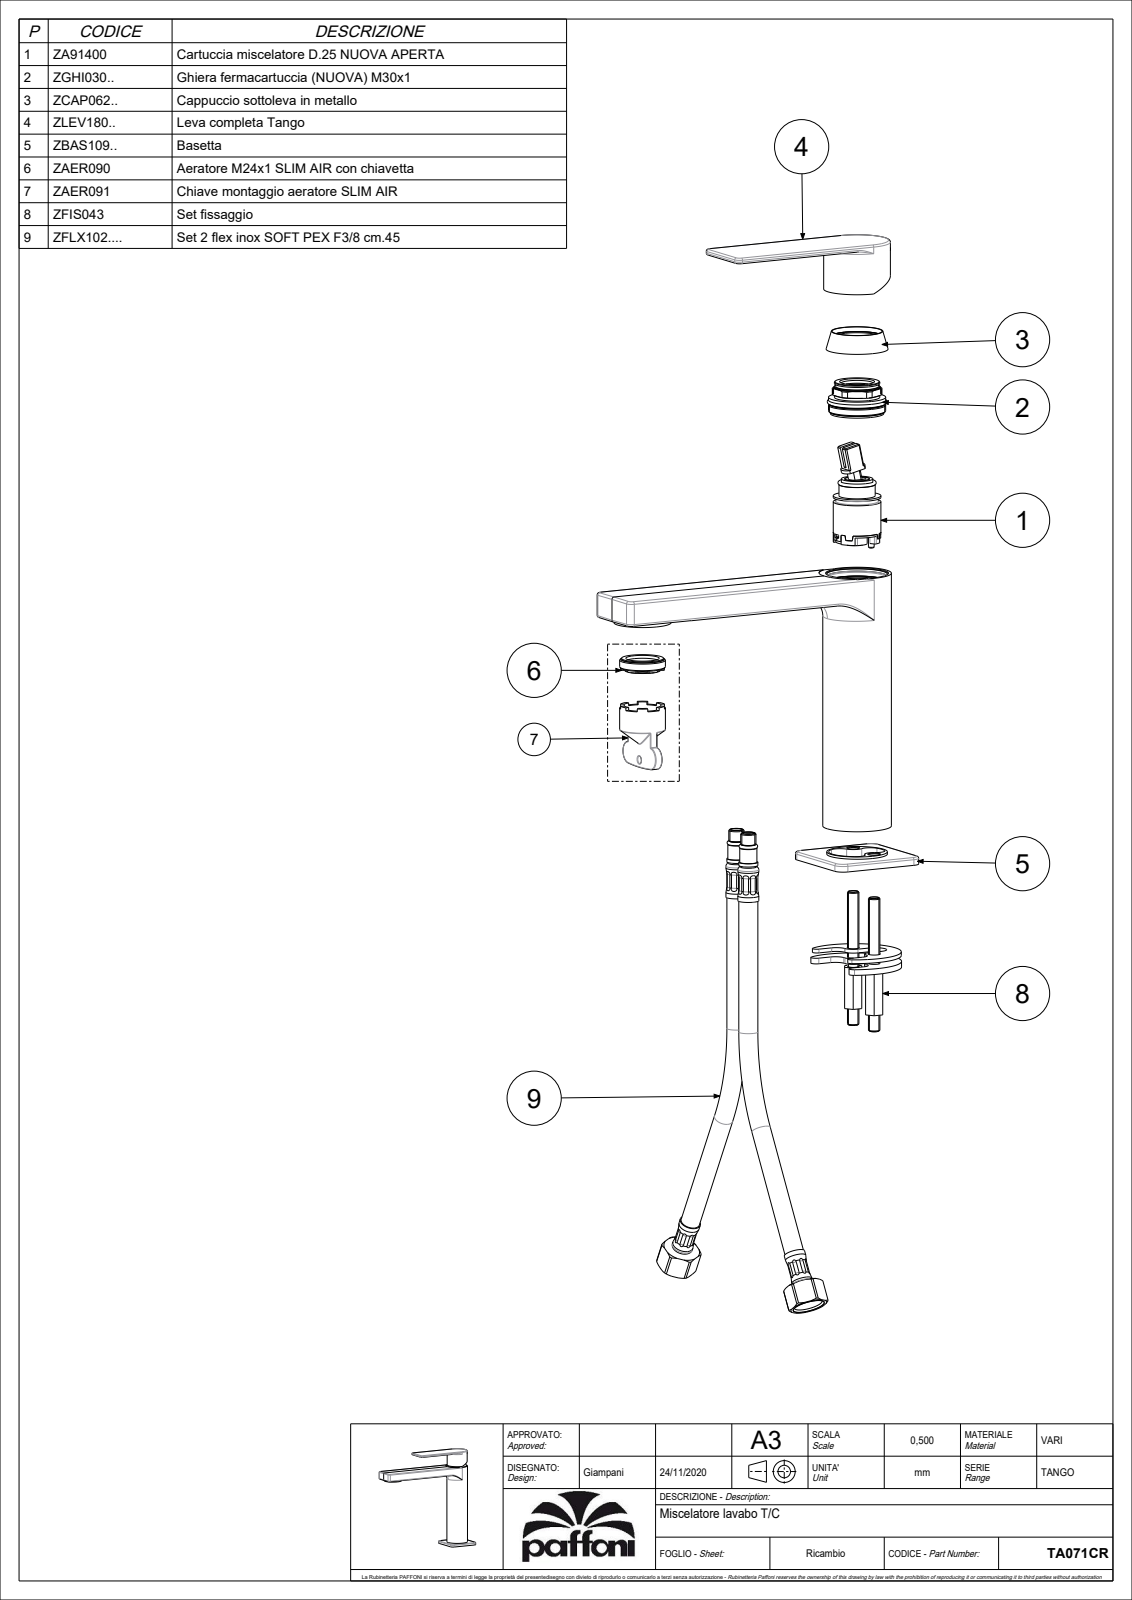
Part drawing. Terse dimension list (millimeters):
name: TA071CR
written by: CREO PARAMETRIC BY PTC INC, 2020044 (CONFIG_CONTROL_DESIGN)
unit: mm
bodies: 2 solids, 477 faces (132 planar, 162 cylindrical, 183 other)
size: 173.5 × 166.2 × 50
volume: 116 220 mm³; area: 72 907 mm²
holes: 2× ⌀4.2, 2× ⌀5, 2× ⌀6.2, 1× ⌀3, 1× ⌀17.5, 1× ⌀24.8, 1× ⌀26.2, 1× ⌀28, 1× ⌀29, 1× ⌀29.29, 1× ⌀30.6, 1× ⌀31.7
bosses: 1× ⌀41.8, 1× ⌀36, 1× ⌀35, 1× ⌀31.8, 1× ⌀30, 1× ⌀25, 1× ⌀18.5, 1× ⌀7.6
rounds: 22× R1.68, 10× R1, 10× R5, 8× R1.2, 8× R3, 6× R2.17, 2× R0.99, 2× R1.5
face distances: 13.5, 3, 163.2, 166.2, 36, 162.2, 4, 159.2, 40.4, 24.5
hole spacings: 11.7, 13.04, 134.45, 11, 22, 130, 141
